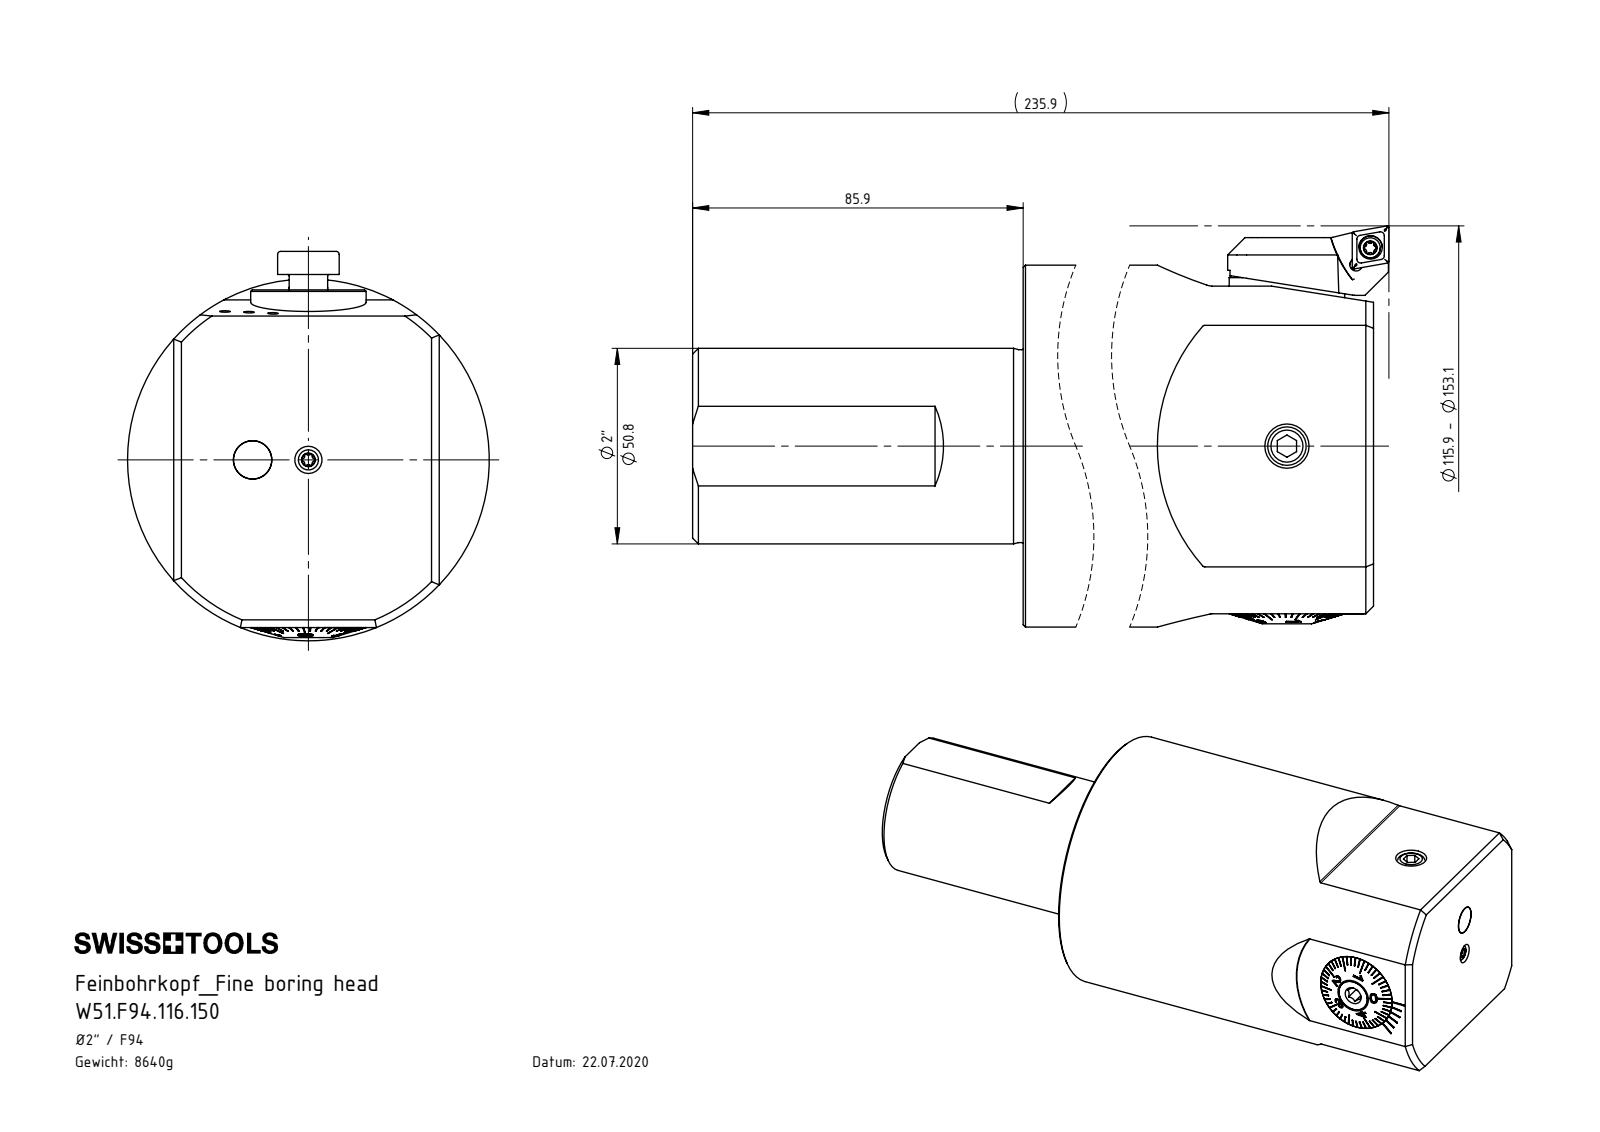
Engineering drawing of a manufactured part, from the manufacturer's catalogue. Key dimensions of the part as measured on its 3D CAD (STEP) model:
Part name (STEP PRODUCT): W51-F94.AA3.150_A_bohrungen gefllt; DIN 3771 - 25x1.5; ISO 4026 - M10 x 16; F94-BG1.DA3.030_A (+8 more)
STEP written by: SolidWorks 2017 (AUTOMOTIVE_DESIGN)
Units: millimetres
Bodies: 13 solids, 565 faces (305 planar, 82 cylindrical, 178 other)
Overall size (bounding box): 231.9 × 101.15 × 94
Volume: 1 095 000 mm³ · Surface area: 106 283 mm²
Round holes (diameter × count): ⌀2.5 ×3, ⌀4.2 ×3, ⌀3.3 ×2, ⌀8.5 ×2, ⌀5 ×1, ⌀8 ×1, ⌀10 ×1, ⌀10.7 ×1, ⌀11.4 ×1, ⌀12 ×1, ⌀12.4 ×1, ⌀13 ×1
Round bosses / shafts (diameter × count): ⌀10 ×2, ⌀94 ×1, ⌀50.8 ×1, ⌀50.1 ×1, ⌀30 ×1, ⌀29.98 ×1, ⌀29.9 ×1, ⌀25 ×1
Partial cylindrical surfaces — rounded edges, fillets, slot ends (radius × count): R0.34 ×6, R0.59 ×6, R2.5 ×6, R2 ×4, R3.2 ×3, R0.5 ×2, R0.8 ×2, R1 ×1
Main face-to-face distances: 146, 69, 85.9, 231.9, 57.2, 11.8, 6.5, 78.6, 85.1, 2.6
Hole centre spacings: 14.5
